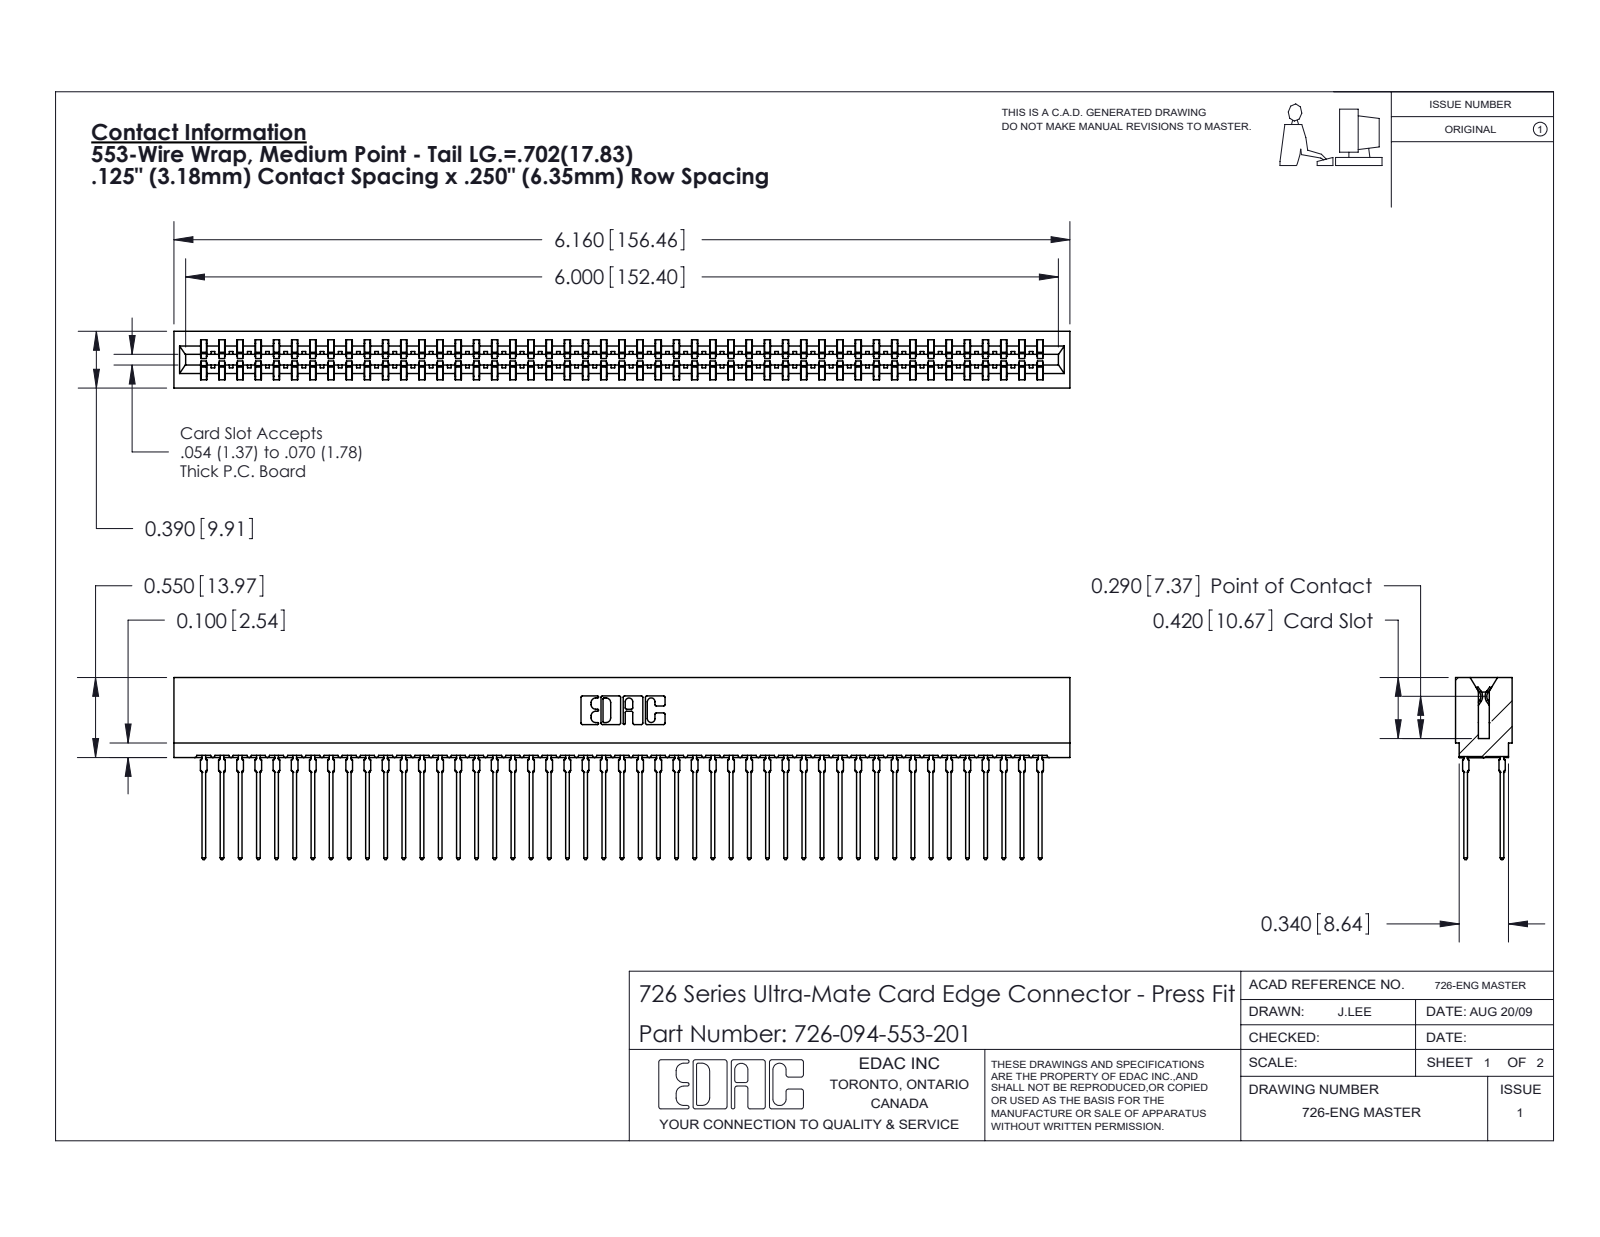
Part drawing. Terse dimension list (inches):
name: 726 Part_.515 Slot Depth - 01; 726-094-553-201; 746-292-001_553
written by: SolidWorks 2020 (CONFIG_CONTROL_DESIGN)
unit: in
bodies: 95 solids, 8510 faces (4379 planar, 1687 cylindrical, 2444 other)
size: 6.16 × 1.251 × 0.39
volume: 0.903 in³; area: 41.3 in²
rounds: 188× R0.021, 48× R0.015, 22× R0.01, 8× R0.005, 8× R0.011, 6× R0.007, 6× R0.031, 3× R0.026
face distances: 0.057, 0.333, 0.025, 0.307, 0.25, 0.083, 0.39, 0.275, 0.225, 0.365
